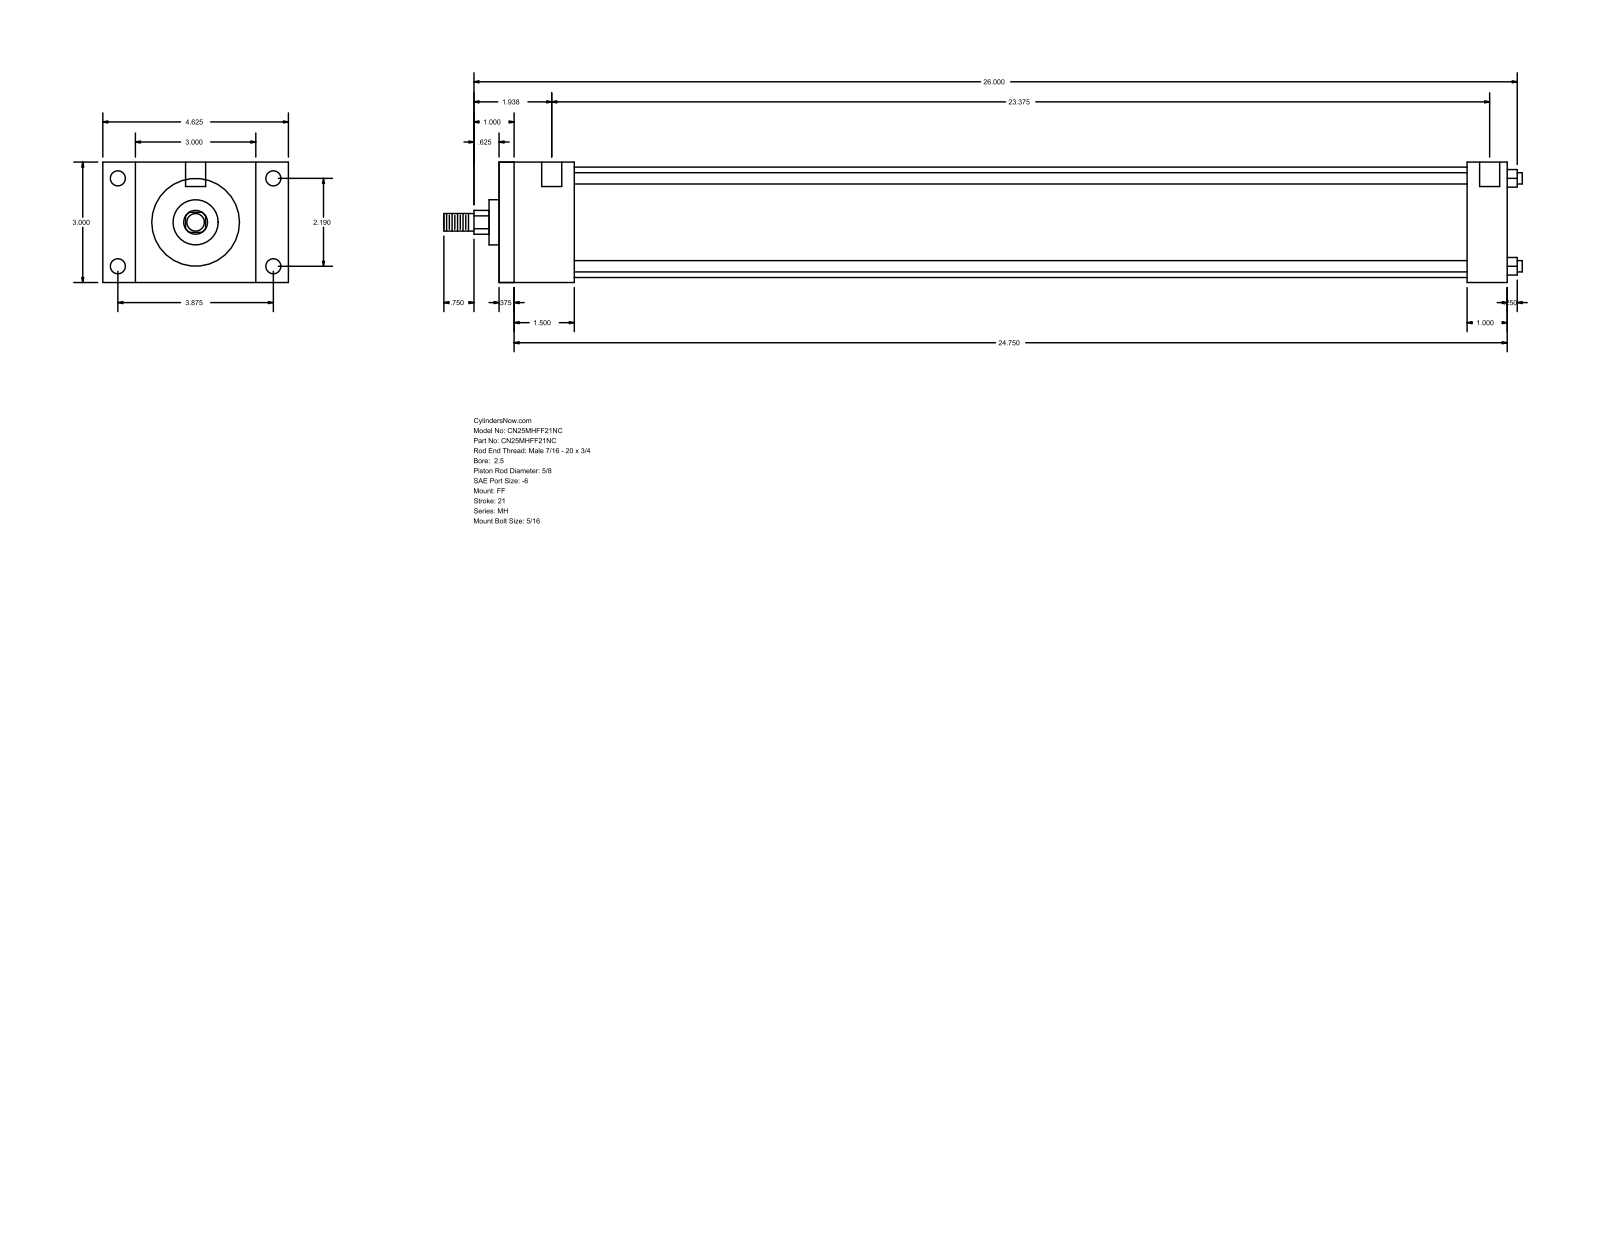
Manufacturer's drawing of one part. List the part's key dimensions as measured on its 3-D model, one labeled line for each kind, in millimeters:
Part name (STEP PRODUCT): MH_FF__0250_0.625
STEP written by: GSSL Pune (CONFIG_CONTROL_DESIGN)
Units: millimetres
Bodies: 0 solids, 92 faces (64 planar, 28 cylindrical, 0 other)
Overall size (bounding box): 682.62 × 117.47 × 76.2
Round holes (diameter × count): ⌀5.56 ×4, ⌀9.53 ×4, ⌀12.7 ×2
Round bosses / shafts (diameter × count): ⌀7.14 ×4, ⌀69.85 ×1, ⌀28.57 ×1, ⌀15.88 ×1, ⌀11.11 ×1
Partial cylindrical surfaces — rounded edges, fillets, slot ends (radius × count): R7.54 ×1
Main face-to-face distances: 76.2, 638.17, 628.65, 9.52, 25.4, 47.62, 612.77, 38.1, 603.25, 565.15
Hole centre spacings: 55.62, 98.42, 113.05, 601.66, 3.17, 4.76, 593.73, 596.9
